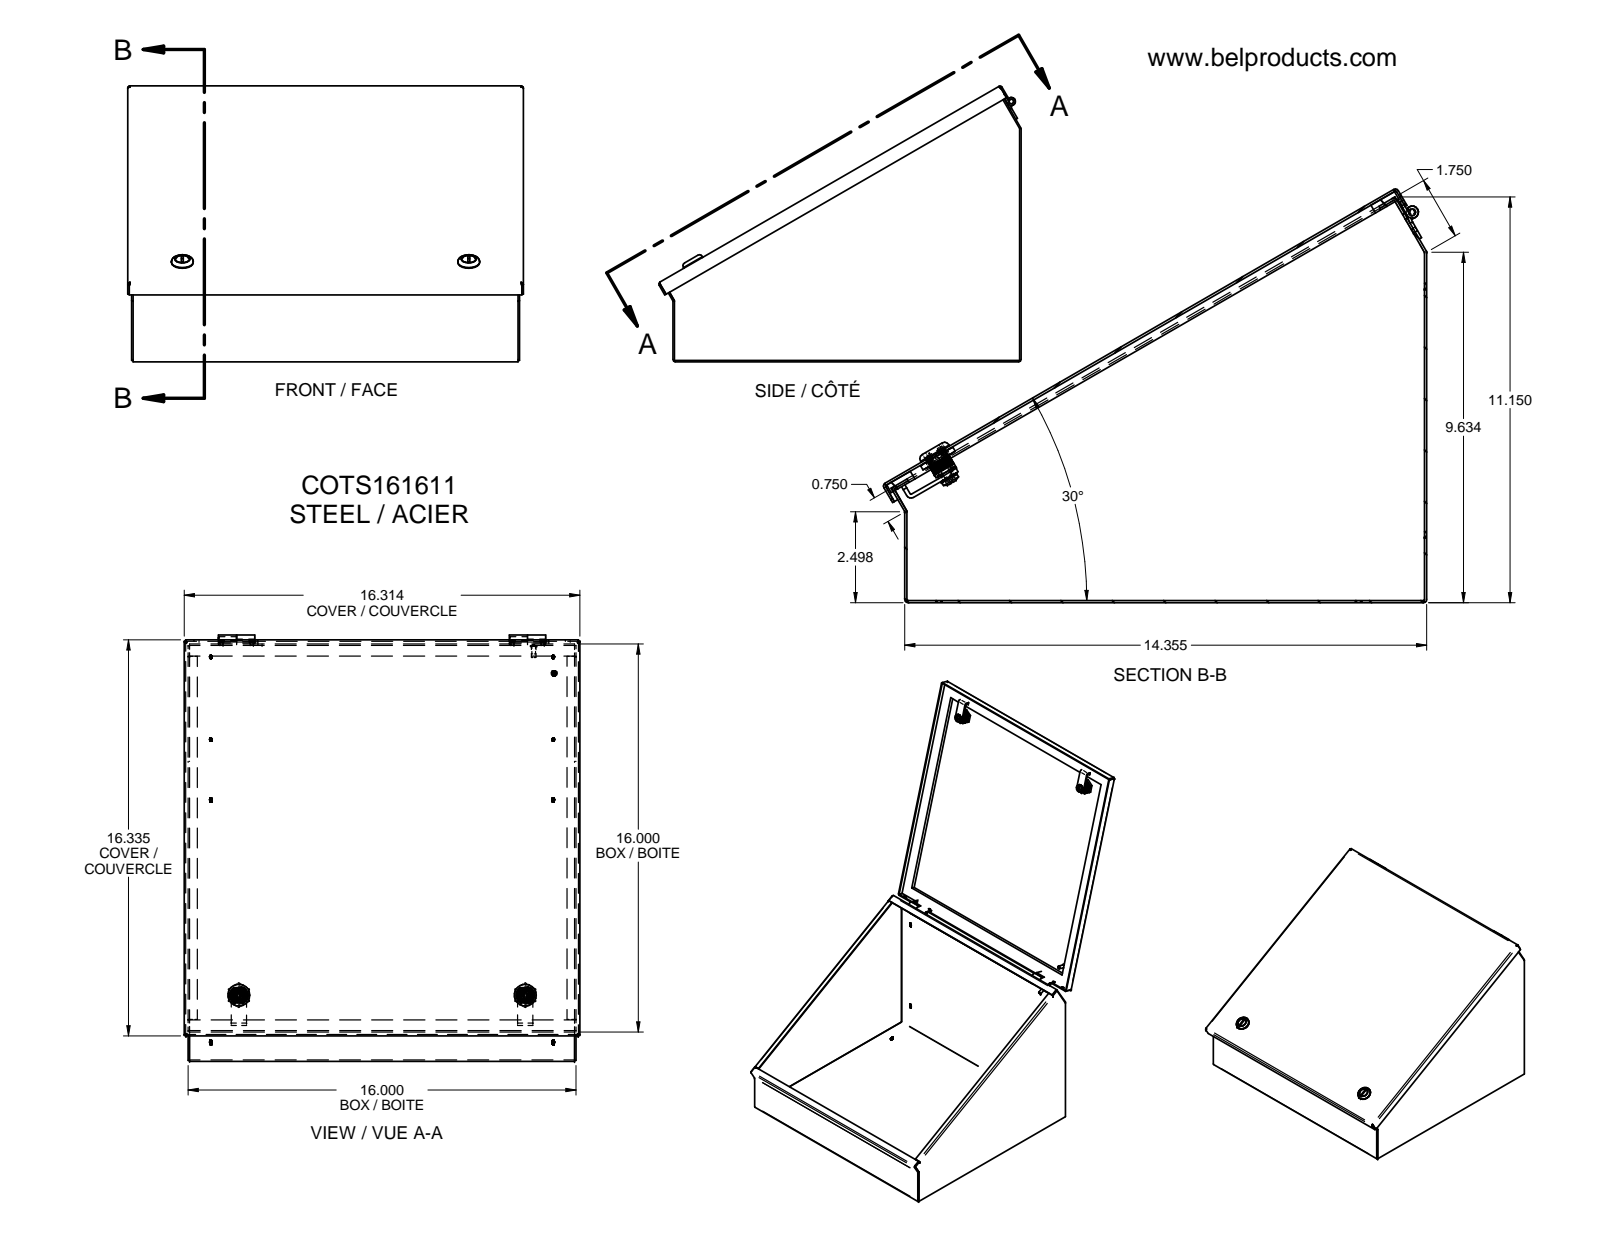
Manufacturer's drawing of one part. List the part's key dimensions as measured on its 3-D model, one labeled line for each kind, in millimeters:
Part name (STEP PRODUCT): LOCK AVEC TOURNEVIS TYPE 4-12 SANS CAME-oa8; HOSING-oa0; INSERT POUR TOURNEVIS-oa1; NOIX DE FIXATION-oa2 (+8 more)
STEP written by: Unknown (AUTOMOTIVE_DESIGN)
Units: millimetres
Bodies: 39 solids, 2321 faces (1412 planar, 309 cylindrical, 600 other)
Overall size (bounding box): 414.38 × 379.47 × 288.84
Volume: 1 552 000 mm³ · Surface area: 1 780 000 mm²
Round holes (diameter × count): ⌀3.17 ×10, ⌀3.3 ×8, ⌀9.53 ×8, ⌀3.16 ×6, ⌀5.11 ×2, ⌀6.99 ×2, ⌀9.1 ×2, ⌀11.18 ×2, ⌀12.83 ×2, ⌀15.8 ×2, ⌀17.46 ×2, ⌀4.29 ×1
Round bosses / shafts (diameter × count): ⌀3.02 ×10, ⌀6.35 ×8, ⌀5.56 ×8, ⌀0.79 ×8, ⌀3.17 ×6, ⌀22.86 ×2, ⌀22.61 ×2, ⌀15.75 ×2
Partial cylindrical surfaces — rounded edges, fillets, slot ends (radius × count): R9.53 ×22, R0.25 ×16, R0.81 ×13, R2.34 ×12, R9.42 ×4, R6.22 ×2, R6.6 ×2, R6.99 ×2
Main face-to-face distances: 1.53, 1.52, 12.84, 16.27, 404.88, 14.36, 14.75, 1.91, 1.9, 14.37
Hole centre spacings: 31.75, 358.74, 358.77, 23.01, 23.02, 304.8, 304.81, 305.67
